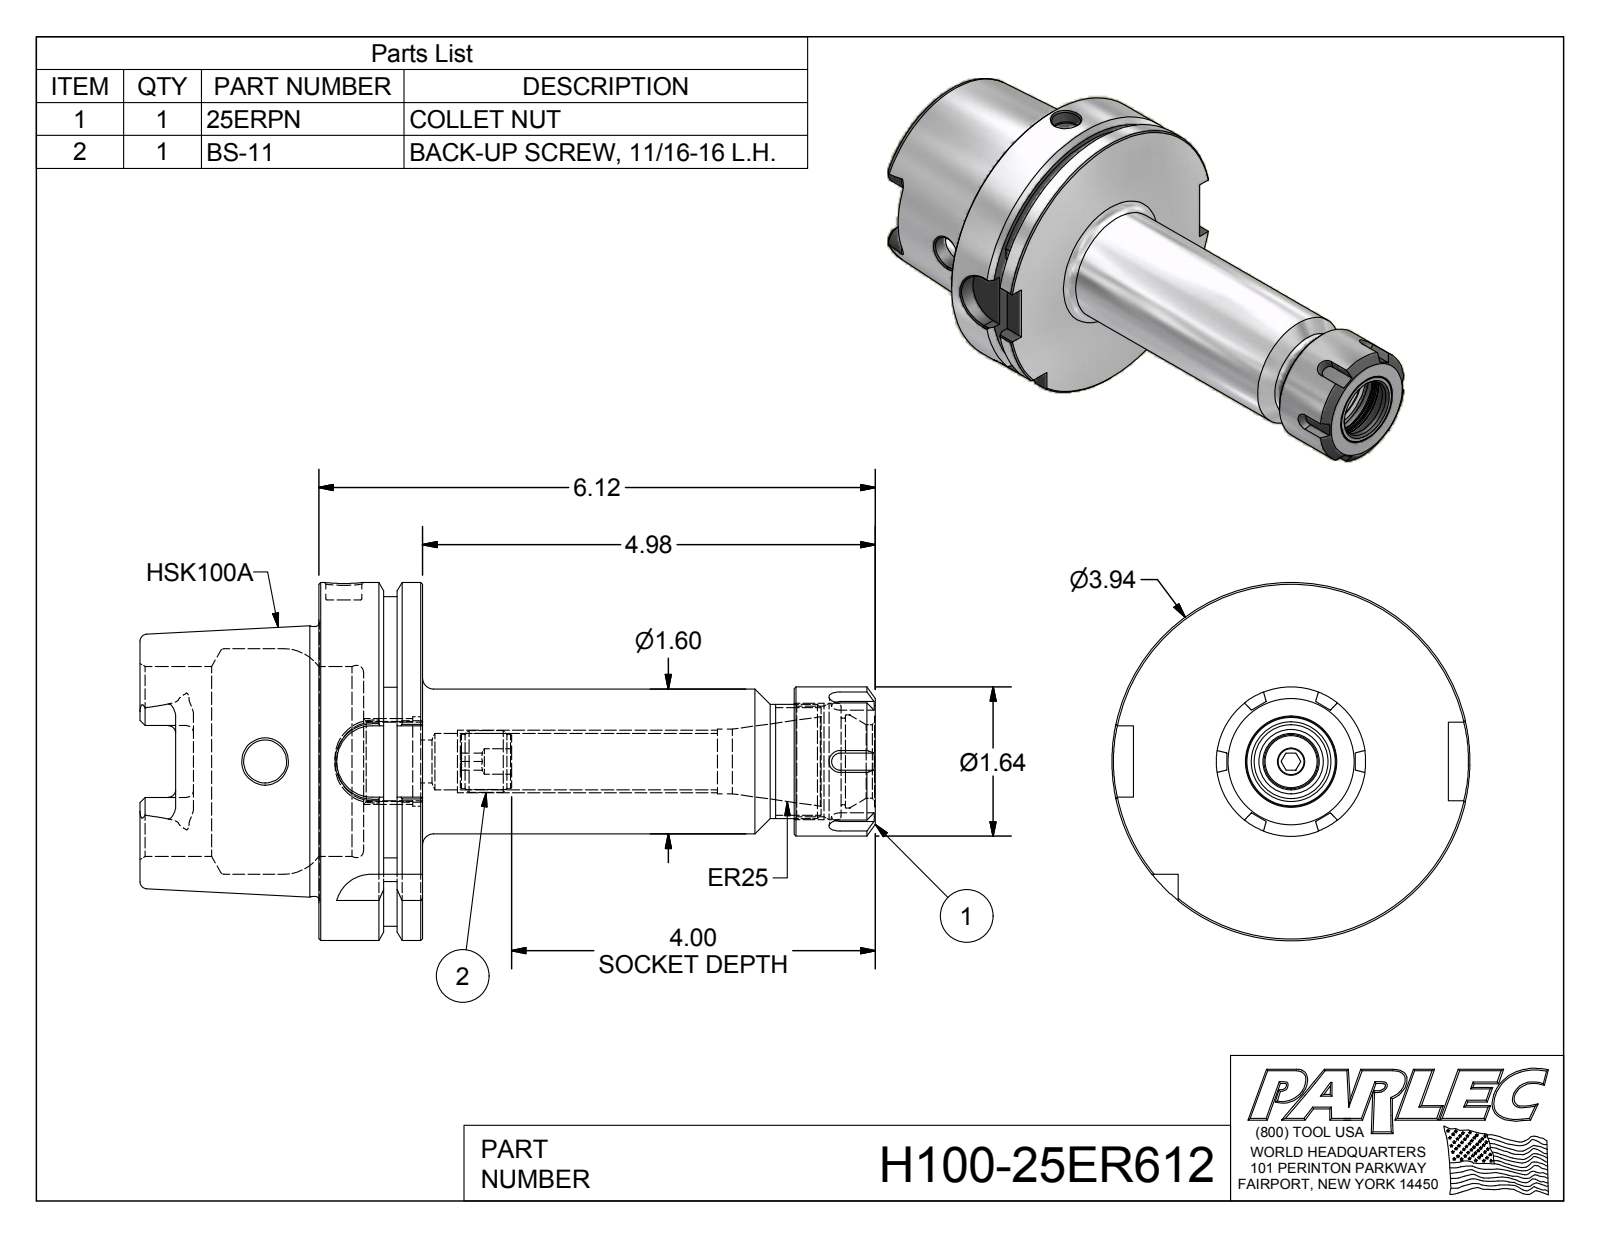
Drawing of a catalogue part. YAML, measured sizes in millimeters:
part_name: "H100-25ER612; H100-25ER6-1; 25ERPN; BS-11"
step_written_by: "Autodesk Inventor 2012 (AUTOMOTIVE_DESIGN)"
units: millimeters
bodies: {solids: 3, faces: 195, planar: 74, cylindrical: 45, other: 76}
overall_size: [205.5, 100, 100]
volume: 381500
surface_area: 77230
round_holes:
  - {diameter: 12, count: 2}
  - {diameter: 7.1, count: 1}
  - {diameter: 10, count: 1}
  - {diameter: 15.7, count: 1}
  - {diameter: 18, count: 1}
  - {diameter: 20.6, count: 1}
  - {diameter: 22.4, count: 1}
  - {diameter: 24.1, count: 1}
  - {diameter: 25, count: 1}
  - {diameter: 26.1, count: 1}
  - {diameter: 30.9, count: 1}
  - {diameter: 32.5, count: 1}
round_bosses_or_shafts:
  - {diameter: 100, count: 1}
  - {diameter: 75.4, count: 1}
  - {diameter: 41.7, count: 1}
  - {diameter: 40.5, count: 1}
  - {diameter: 32, count: 1}
  - {diameter: 17.3, count: 1}
  - {diameter: 15.1, count: 1}
partial_cylinders:
  - {radius: 2, count: 6}
  - {radius: 4.9, count: 4}
  - {radius: 10, count: 4}
  - {radius: 46, count: 1}
face_to_face_distances: [29, 12.5, 16.5, 50, 62.5, 79, 71.9, 21.9, 9.4, 7.1]
